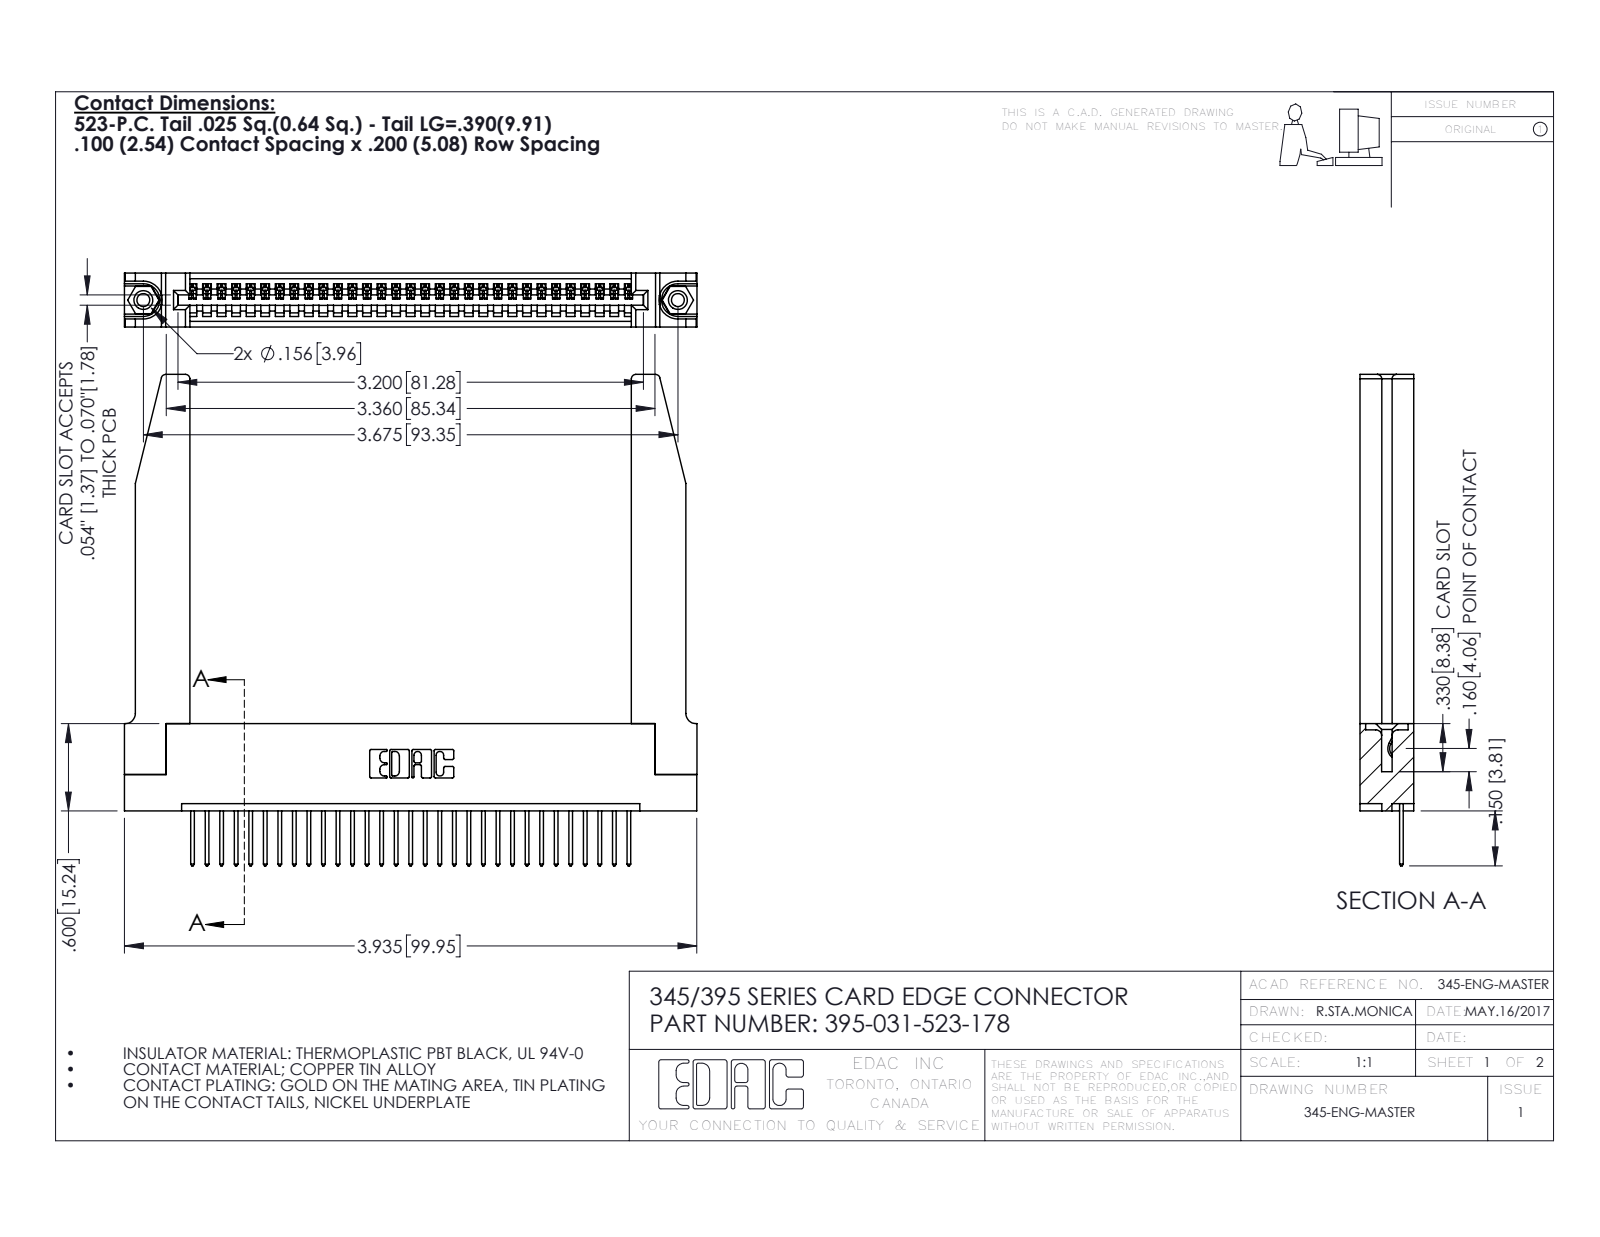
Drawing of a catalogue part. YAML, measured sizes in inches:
part_name: "345-292-001_345-293-123; 395-031-523-178; 345-250-001_345-250-001-102; 345-220-078_345-220-078 (+1 more)"
step_written_by: "SolidWorks 2016 (CONFIG_CONTROL_DESIGN)"
units: inches
bodies: {solids: 36, faces: 2158, planar: 1462, cylindrical: 644, other: 52}
overall_size: [3.936, 3.377, 0.37]
volume: 1.047
surface_area: 29.78
round_holes:
  - {diameter: 0.089, count: 2}
  - {diameter: 0.125, count: 2}
  - {diameter: 0.156, count: 2}
  - {diameter: 0.064, count: 1}
round_bosses_or_shafts:
  - {diameter: 0.155, count: 2}
partial_cylinders:
  - {radius: 0.006, count: 62}
  - {radius: 0.01, count: 62}
  - {radius: 0.01, count: 22}
  - {radius: 0.03, count: 8}
  - {radius: 0.007, count: 6}
  - {radius: 0.031, count: 6}
  - {radius: 0.026, count: 3}
  - {radius: 0.031, count: 2}
face_to_face_distances: [0.37, 0.072, 0.298, 0.2, 0.098, 0.272, 0.025, 0.15, 0.148, 0.225]
hole_center_spacings: [0.27, 3.44, 3.675]
